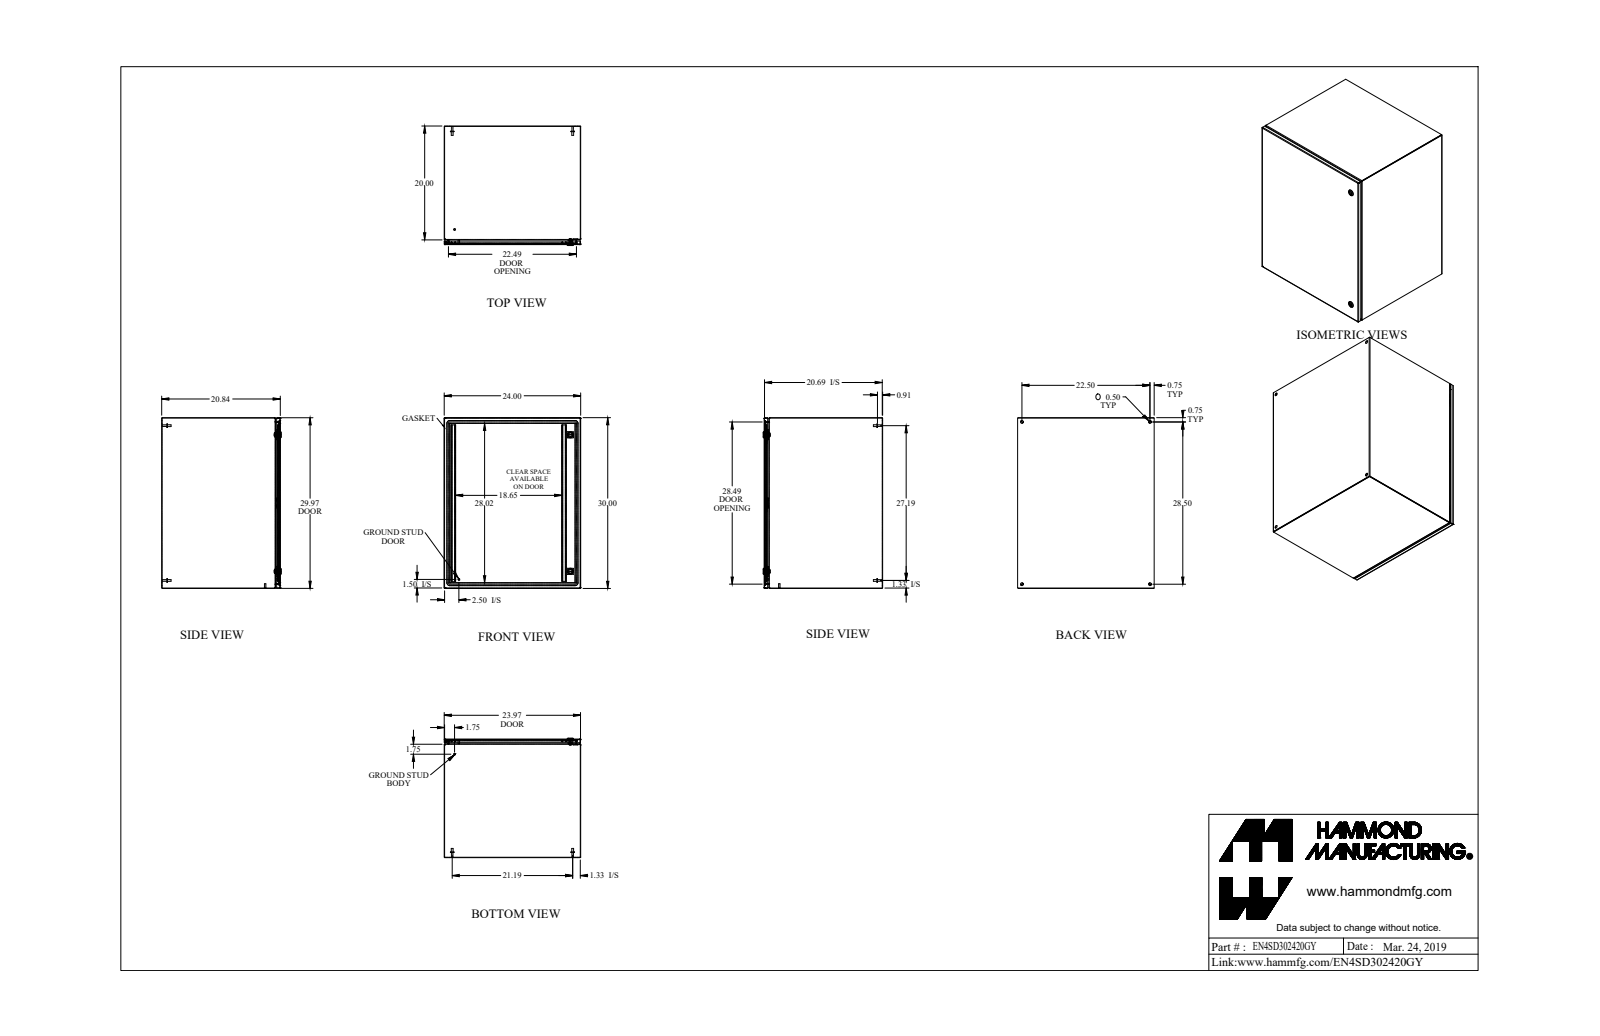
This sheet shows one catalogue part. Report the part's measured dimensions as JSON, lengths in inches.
{"part_name": "EN4SD302420GY", "step_written_by": "SolidWorks 2019 (AUTOMOTIVE_DESIGN)", "units": "inches", "bodies": {"solids": 33, "faces": 838, "planar": 399, "cylindrical": 283, "other": 156}, "overall_size": [30, 24, 20.997], "volume_in3": 288.1, "surface_area_in2": 8074, "round_holes": [[0.5, 4], [0.232, 2], [0.625, 2], [0.785, 2], [0.172, 1], [0.24, 1], [0.242, 1]], "round_bosses_or_shafts": [[0.625, 4], [0.313, 4], [0.27, 4], [1.1, 2], [0.525, 2], [0.281, 2], [0.25, 2], [0.455, 1]], "partial_cylinders_radius": [[0.036, 14], [0.108, 14], [0.043, 12], [0.081, 12], [0.312, 12], [0.1, 8], [0.006, 6], [0.062, 6]], "face_to_face_distances": [0.072, 20.765, 23.928, 29.928, 20.693, 20.837, 23.856, 24, 29.856, 30], "hole_center_spacings": [22.5, 28.5, 36.311, 2.493, 2.494, 21.545, 21.545, 23.999]}
